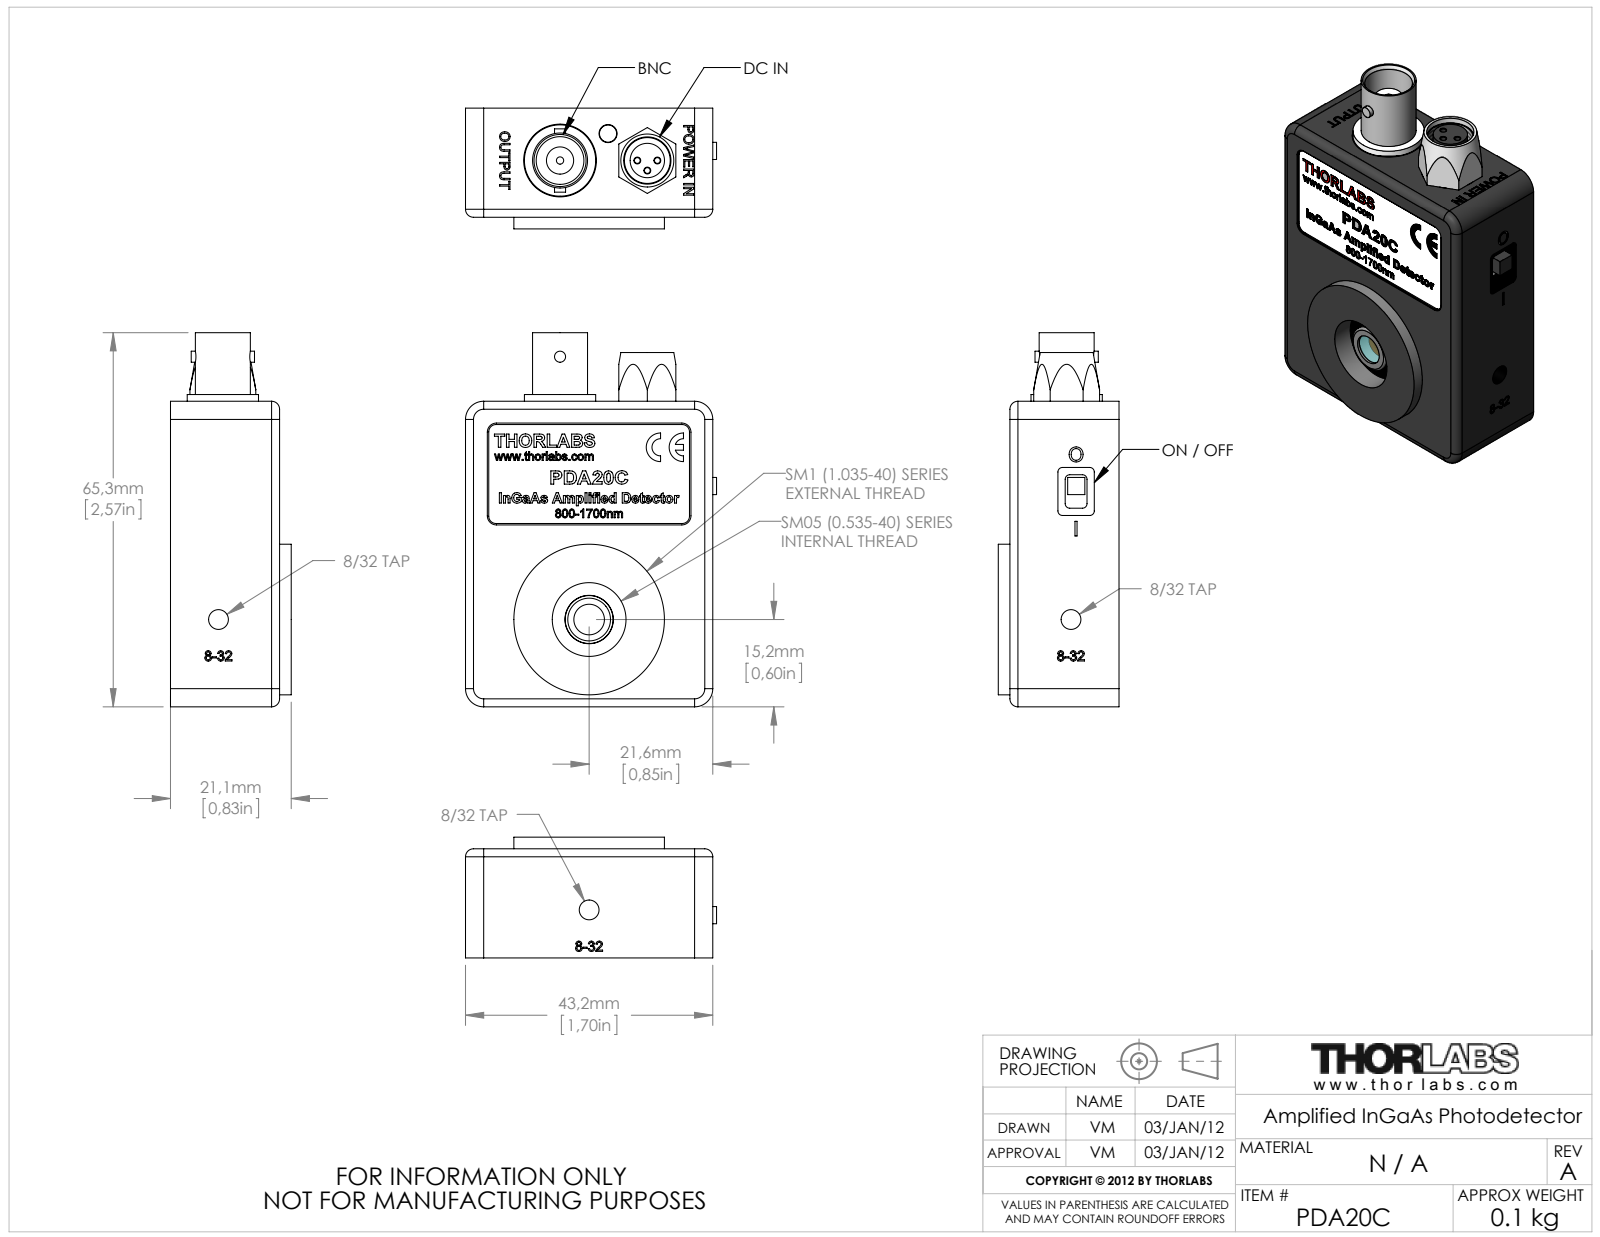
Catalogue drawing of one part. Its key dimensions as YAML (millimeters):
part_name: "LED-3mm; M0092-0575-0A-(M4)-Gehäuse_Etching; PDA20C; S2386-18K-Hamamatsu (+8 more)"
step_written_by: "SolidWorks 2009 (AUTOMOTIVE_DESIGN)"
units: millimeters
bodies: {solids: 16, faces: 1833, planar: 1002, cylindrical: 270, other: 561}
overall_size: [65.3, 43.84, 21.08]
volume: 22330
surface_area: 24337
round_holes:
  - {diameter: 1.6, count: 7}
  - {diameter: 2.4, count: 4}
  - {diameter: 0.46, count: 3}
  - {diameter: 1, count: 3}
  - {diameter: 2.44, count: 3}
  - {diameter: 1.65, count: 2}
  - {diameter: 3.3, count: 2}
  - {diameter: 1.27, count: 1}
  - {diameter: 1.32, count: 1}
  - {diameter: 3.15, count: 1}
  - {diameter: 4.95, count: 1}
  - {diameter: 6, count: 1}
round_bosses_or_shafts:
  - {diameter: 3.8, count: 7}
  - {diameter: 2, count: 7}
  - {diameter: 0.51, count: 6}
  - {diameter: 0.74, count: 2}
  - {diameter: 26.29, count: 1}
  - {diameter: 12.45, count: 1}
  - {diameter: 10.92, count: 1}
  - {diameter: 9.6, count: 1}
partial_cylinders:
  - {radius: 3.17, count: 32}
  - {radius: 3.3, count: 12}
  - {radius: 0.8, count: 10}
  - {radius: 0.79, count: 8}
  - {radius: 2.41, count: 8}
  - {radius: 2.54, count: 5}
  - {radius: 1.27, count: 4}
  - {radius: 1.4, count: 4}
face_to_face_distances: [1.59, 12.06, 10.47, 2.54, 8.87, 10.46, 1.6, 1.27, 18.54, 16.95]
hole_center_spacings: [1.75, 2.54, 1.58, 2.09, 2.47, 3.59, 4.38, 5.14]
